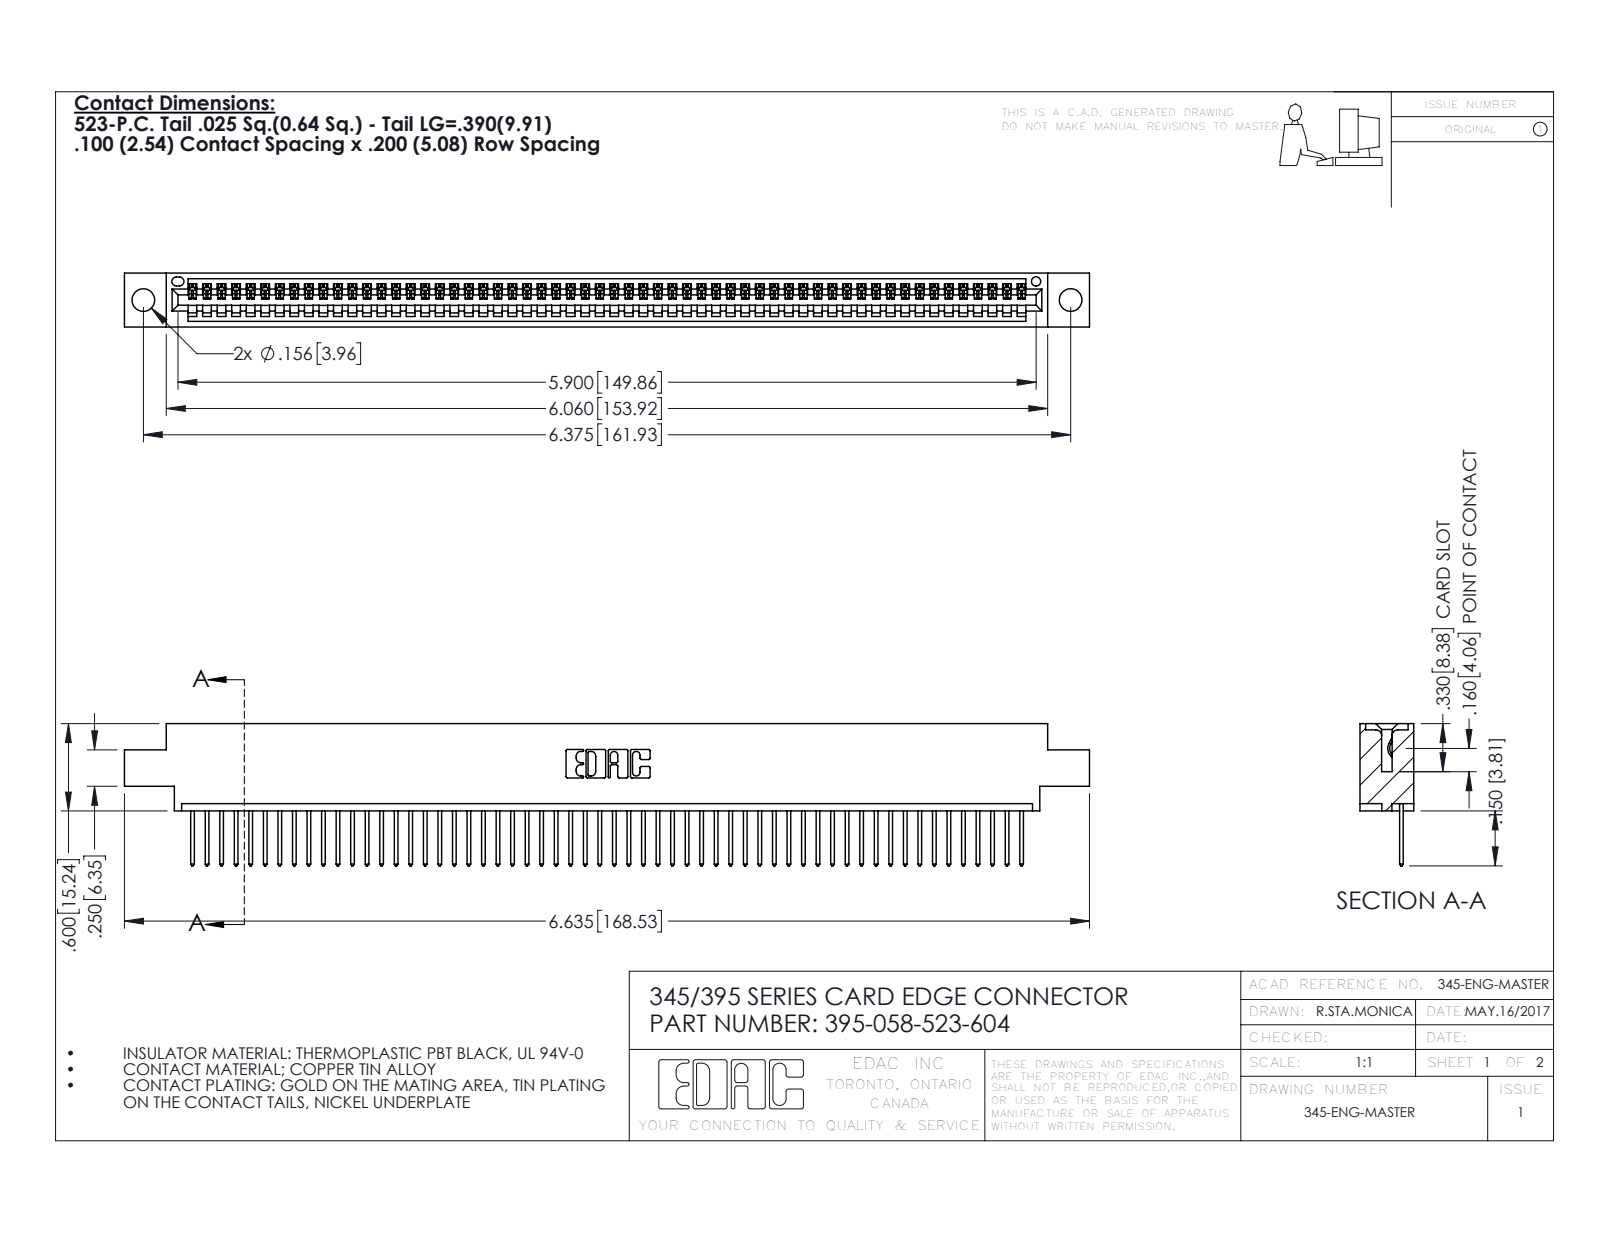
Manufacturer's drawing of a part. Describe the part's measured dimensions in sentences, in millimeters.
The part is named "345-292-001_345-293-123; 345 Part_0.170 Offset - 0.156 Dia-TH; 395-058-523-604". Its 3-D file was written by "SolidWorks 2016 (CONFIG_CONTROL_DESIGN)". It is 59 solids with 3494 faces: 2404 planar, 1090 cylindrical and 0 other. Overall it measures 168.5 by 24.8 by 9.4 millimeters. Its volume is 15 900 cubic millimeters and its surface area 21 370 square millimeters. Round holes: 2 of diameter 4, 1 of diameter 1.6. Partial cylindrical surfaces (rounded edges, fillets, slot ends): 116 of radius 0.2, 116 of radius 0.3, 22 of radius 0.3, 6 of radius 0.2, 6 of radius 0.8, 3 of radius 0.7, 2 of radius 0.8, 2 of radius 1. The main face-to-face distances are 7.6, 1.8, 9.4, 2.5, 6.9, 0.6, 5.1, 5.7, 4.4, 3.8. The hole center spacings are 6.9, 155.9, 161.9.
